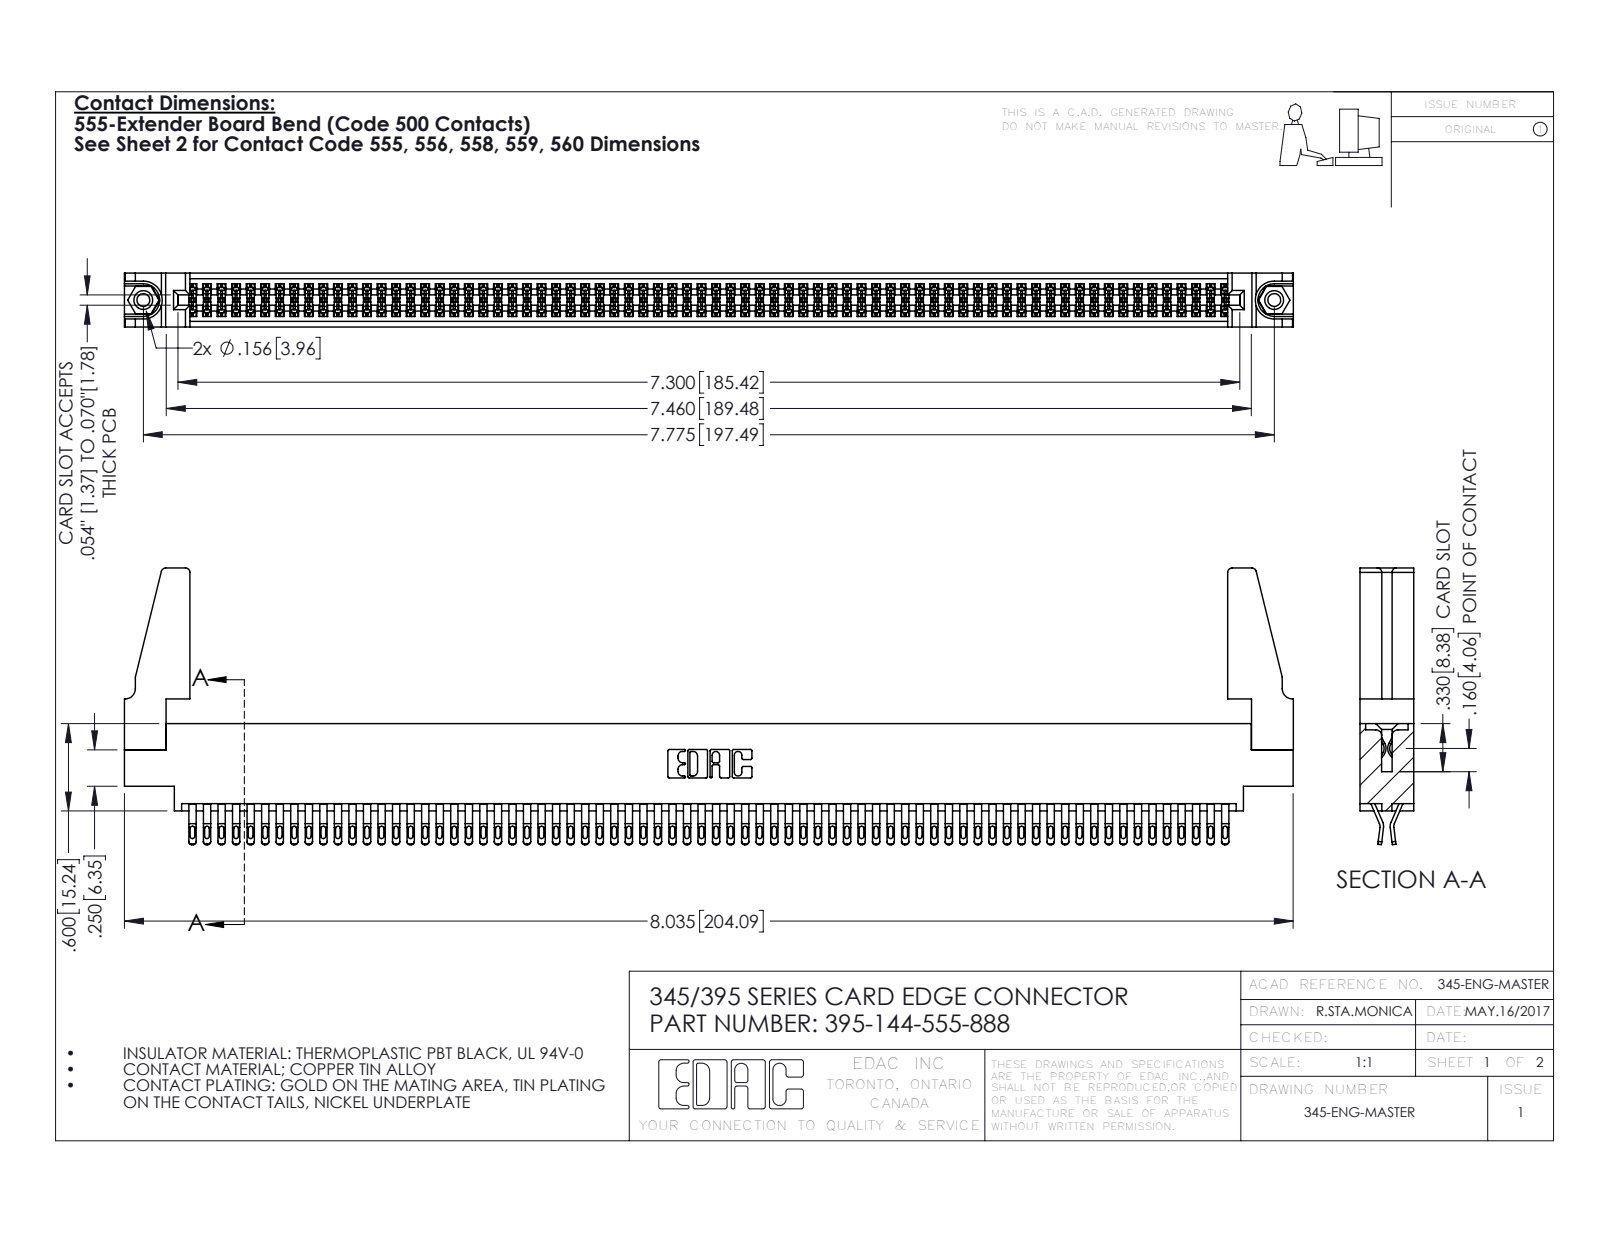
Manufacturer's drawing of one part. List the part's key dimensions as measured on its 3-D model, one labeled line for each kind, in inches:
Part name (STEP PRODUCT): 345 Part_0.170 Offset - 0.156 Dia-TH; 345-292-001_555 Tail; 395-144-555-888; 345-250-001_345-250-001-102 (+1 more)
STEP written by: SolidWorks 2016 (CONFIG_CONTROL_DESIGN)
Units: inches
Bodies: 149 solids, 8318 faces (4620 planar, 3682 cylindrical, 16 other)
Overall size (bounding box): 8.036 × 1.902 × 0.37
Volume: 1.444 in³ · Surface area: 54.98 in²
Round holes (diameter × count): ⌀0.089 ×2, ⌀0.125 ×2, ⌀0.156 ×2, ⌀0.064 ×1
Round bosses / shafts (diameter × count): ⌀0.155 ×2
Partial cylindrical surfaces — rounded edges, fillets, slot ends (radius × count): R0.016 ×360, R0.02 ×288, R0.006 ×216, R0.01 ×22, R0.03 ×8, R0.007 ×6, R0.031 ×6, R0.026 ×3
Main face-to-face distances: 0.072, 0.298, 0.37, 0.025, 0.2, 0.098, 0.272, 0.225, 0.175, 0.149
Hole centre spacings: 0.27, 7.539, 7.775
